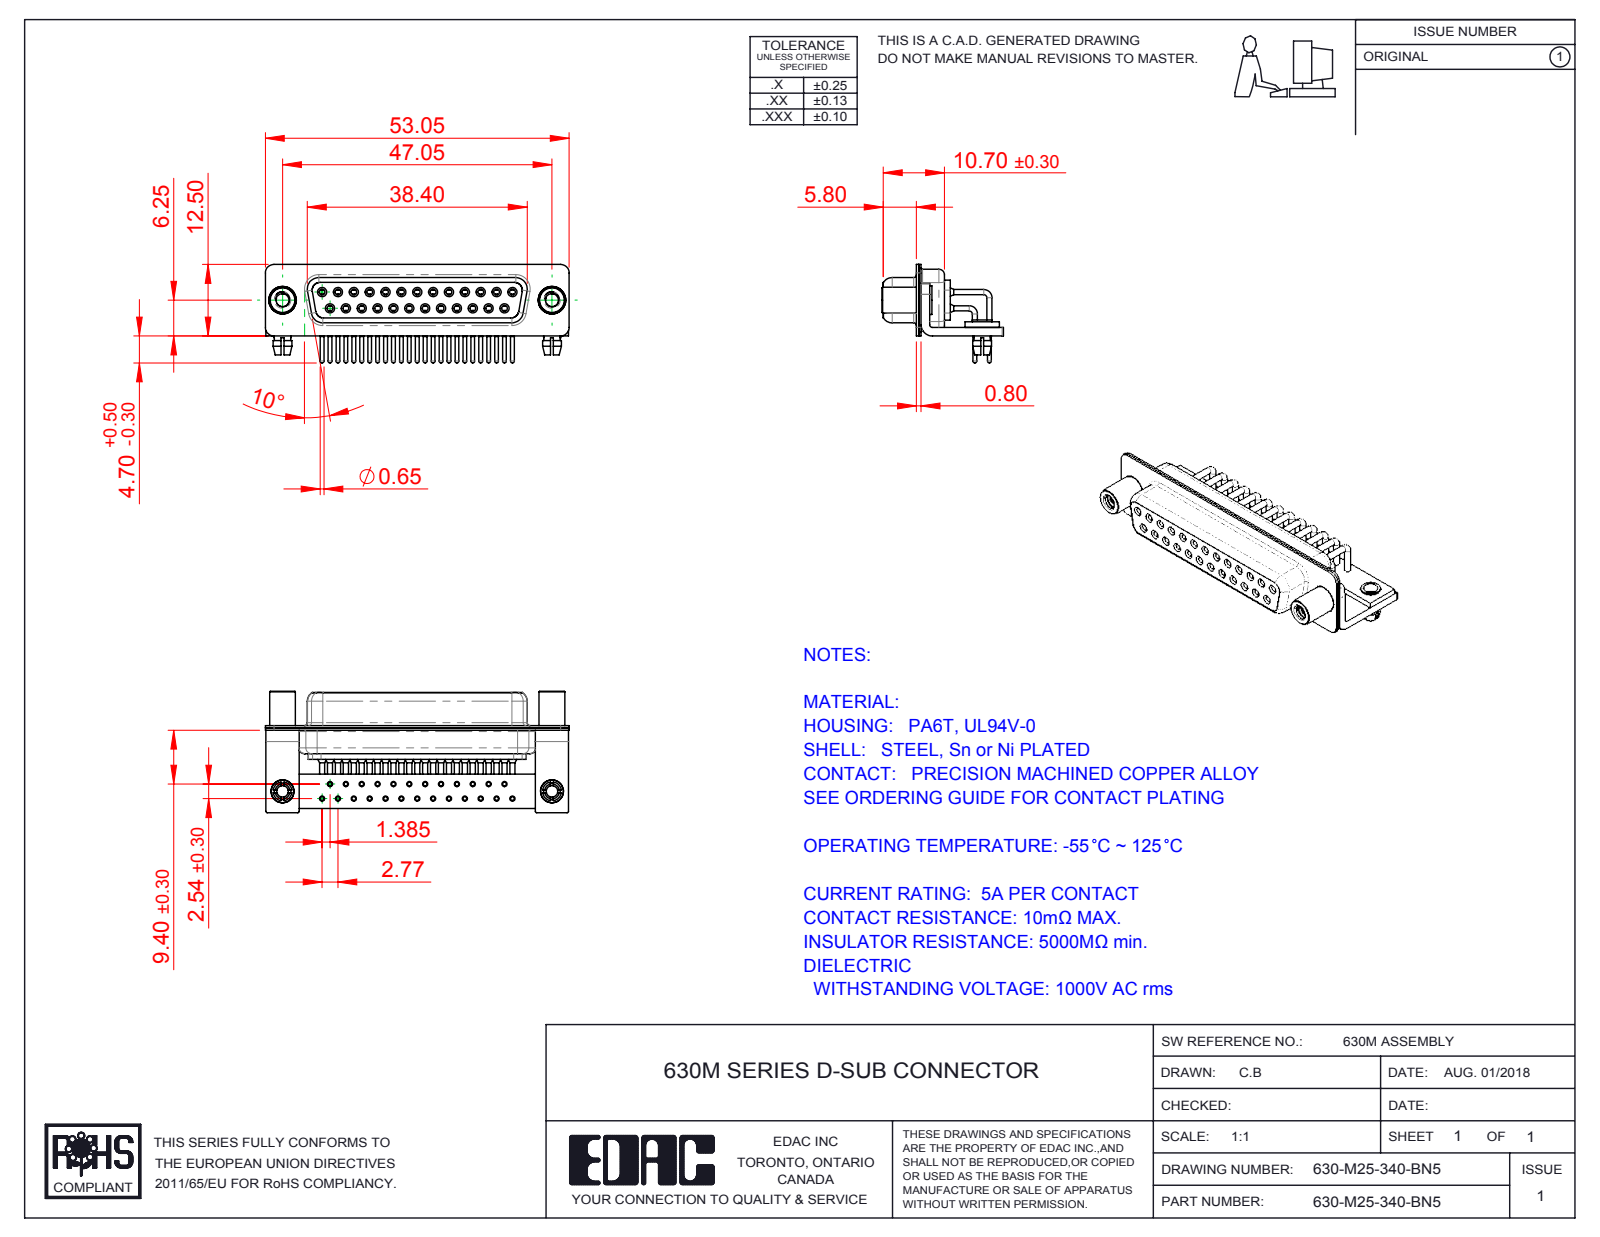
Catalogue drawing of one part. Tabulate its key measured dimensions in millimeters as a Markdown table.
| quantity | value |
| --- | --- |
| part name | 630-M25-340-BN5; 630M 4-40 Threaded Standoff; 630M Stabilizer Bracket; 630M Contact Row 1 (+6 more) |
| STEP written by | SolidWorks 2016 (CONFIG_CONTROL_DESIGN) |
| units | millimeters |
| bodies | 35 solids, 1846 faces (518 planar, 858 cylindrical, 470 other) |
| overall size | 53.05 × 21.2 × 17.2 |
| volume | 4 624 mm³ |
| surface area | 11 662 mm² |
| round holes (diameter × count) | 2 × 27, 0.9 × 25, 1 × 25, 1.1 × 25, 1.7 × 25, 1.8 × 25, 2.26 × 2, 2.5 × 2, 3.2 × 2, 4 × 2, 4.8 × 2 |
| round bosses / shafts (diameter × count) | 1.6 × 25, 1.5 × 25, 0.9 × 25, 0.65 × 25, 5 × 2, 4.9 × 2, 4.5 × 2, 4 × 2 |
| partial cylindrical surfaces (radius × count) | 0.25 × 16, 1.5 × 16, 2 × 13, 1.35 × 10, 1.6 × 8, 0.5 × 5, 0.6 × 4, 0.65 × 4 |
| main face-to-face distances | 0.4, 2.3, 1.9, 9.35, 1.45, 8.95, 0.85, 0.8, 6.2, 1 |
| hole center spacings | 2.77, 5.54, 8.31, 11.08, 13.85, 3.16, 4.87, 16.62 |
